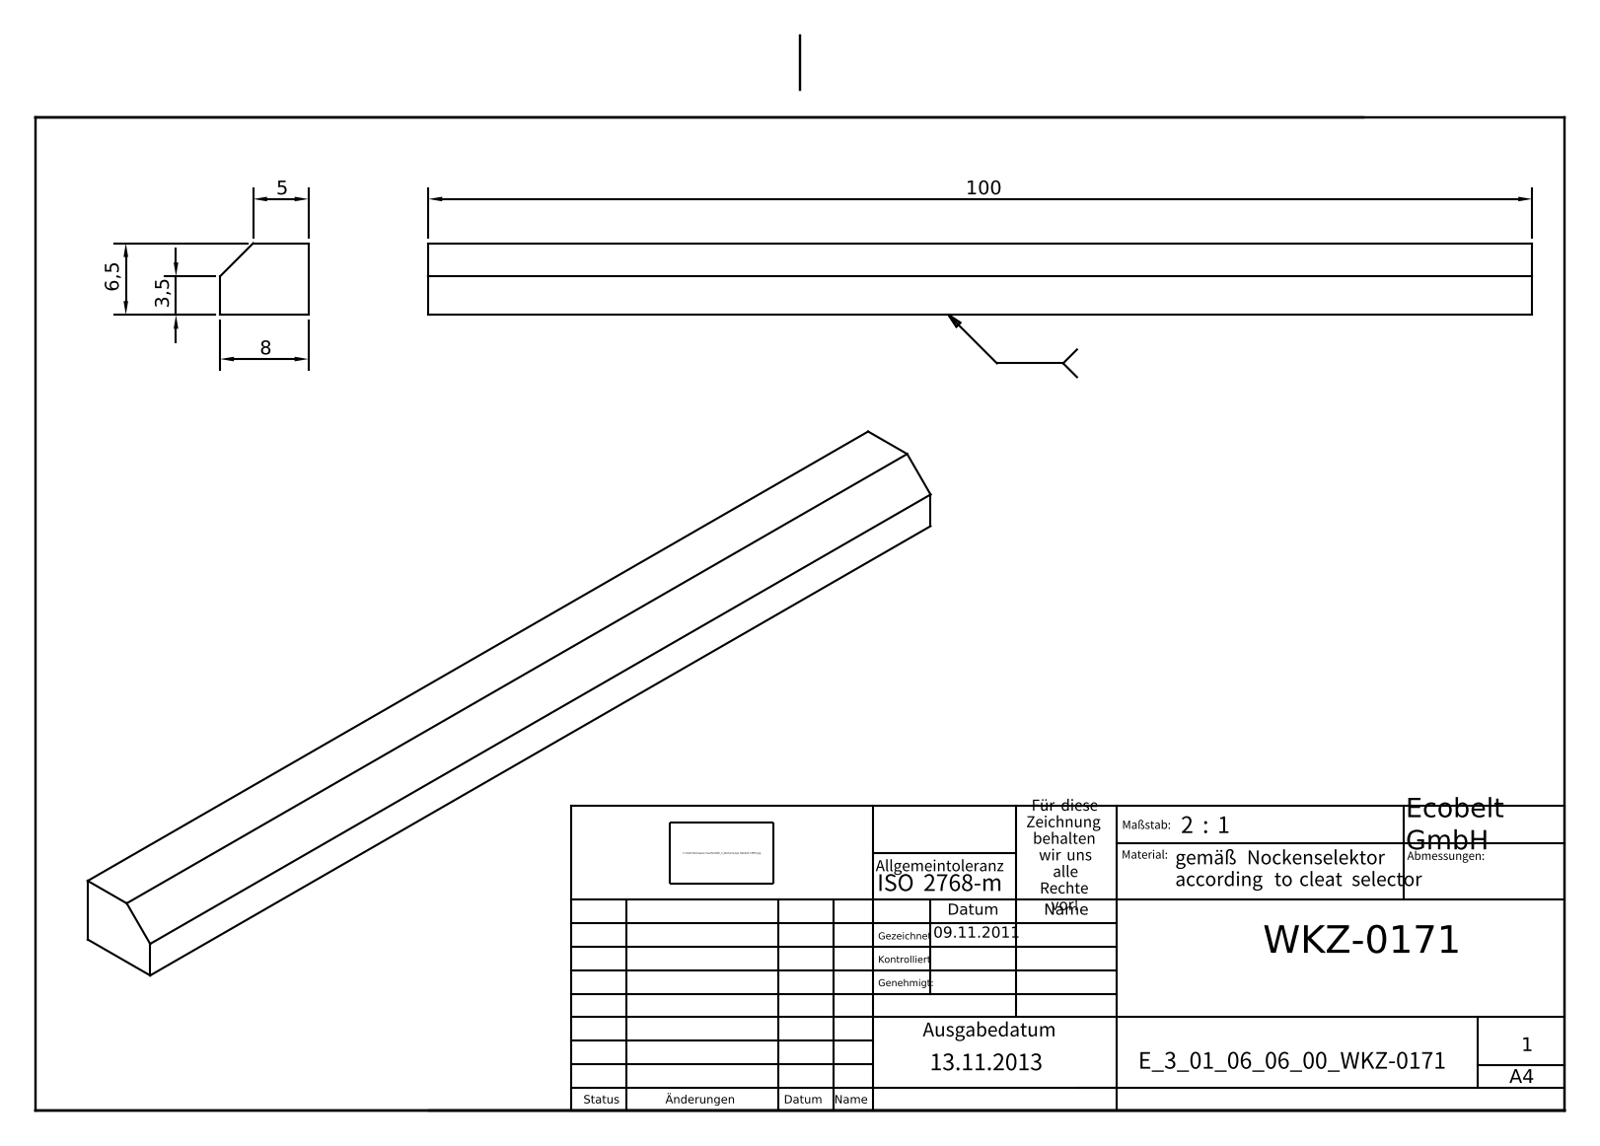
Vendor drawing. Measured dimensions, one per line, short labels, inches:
name: E_3_01_06_06_00_WKZ-0171
written by: Autodesk Inventor 2025 (AUTOMOTIVE_DESIGN)
unit: in
bodies: 1 solid, 7 faces (7 planar, 0 cylindrical, 0 other)
size: 3.937 × 0.315 × 0.256
volume: 0.29 in³; area: 4.369 in²
face distances: 0.256, 0.315, 3.937
